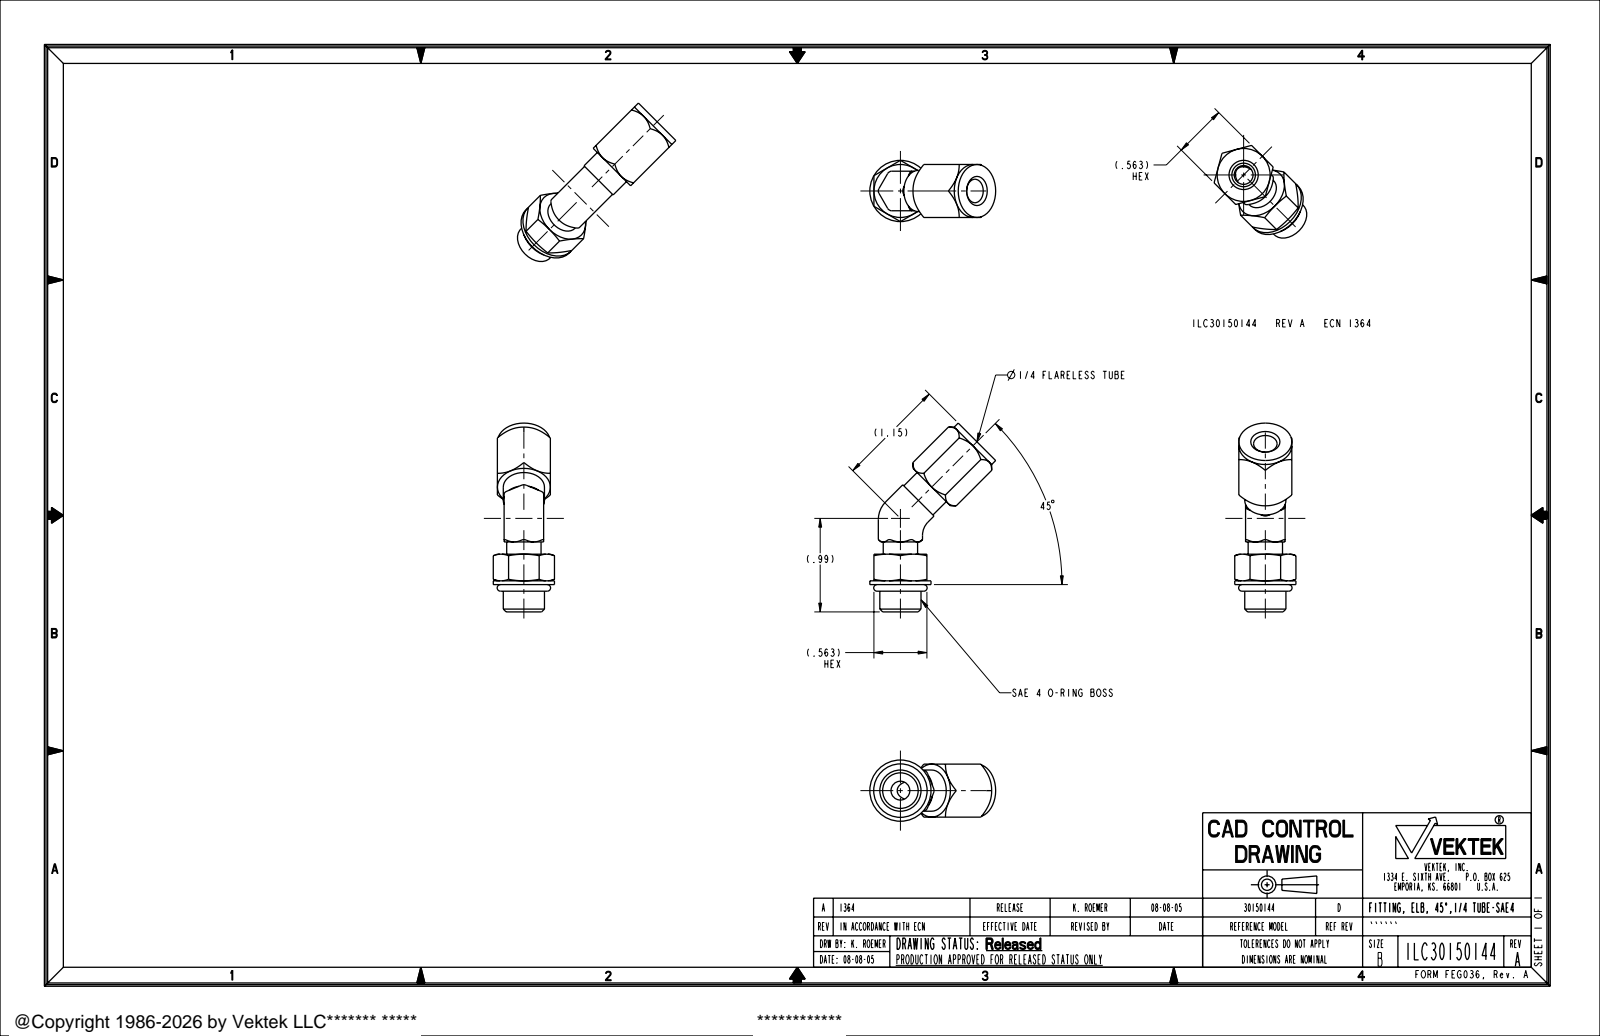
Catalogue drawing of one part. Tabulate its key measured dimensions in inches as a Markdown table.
| quantity | value |
| --- | --- |
| part name | ILC30150144 |
| STEP written by | PRO/ENGINEER BY PARAMETRIC TECHNOLOGY CORPORATION, 2004290 (AUTOMOTIVE_DESIGN_CC2) |
| units | inches |
| bodies | 1 solid, 106 faces (44 planar, 36 cylindrical, 26 other) |
| overall size | 1.986 × 1.161 × 0.65 |
| volume | 0.366 in³ |
| surface area | 6.117 in² |
| round holes (diameter × count) | 0.2 × 2, 0.25 × 1 |
| round bosses / shafts (diameter × count) | 0.437 × 2, 0.65 × 1, 0.563 × 1, 0.365 × 1 |
| partial cylindrical surfaces (radius × count) | 0.05 × 12, 0.2 × 2, 0.3 × 2 |
| main face-to-face distances | 0.563, 0.072, 0.491, 0.42, 0.323, 0.68, 0.04, 0.283, 0.29, 0.33 |
